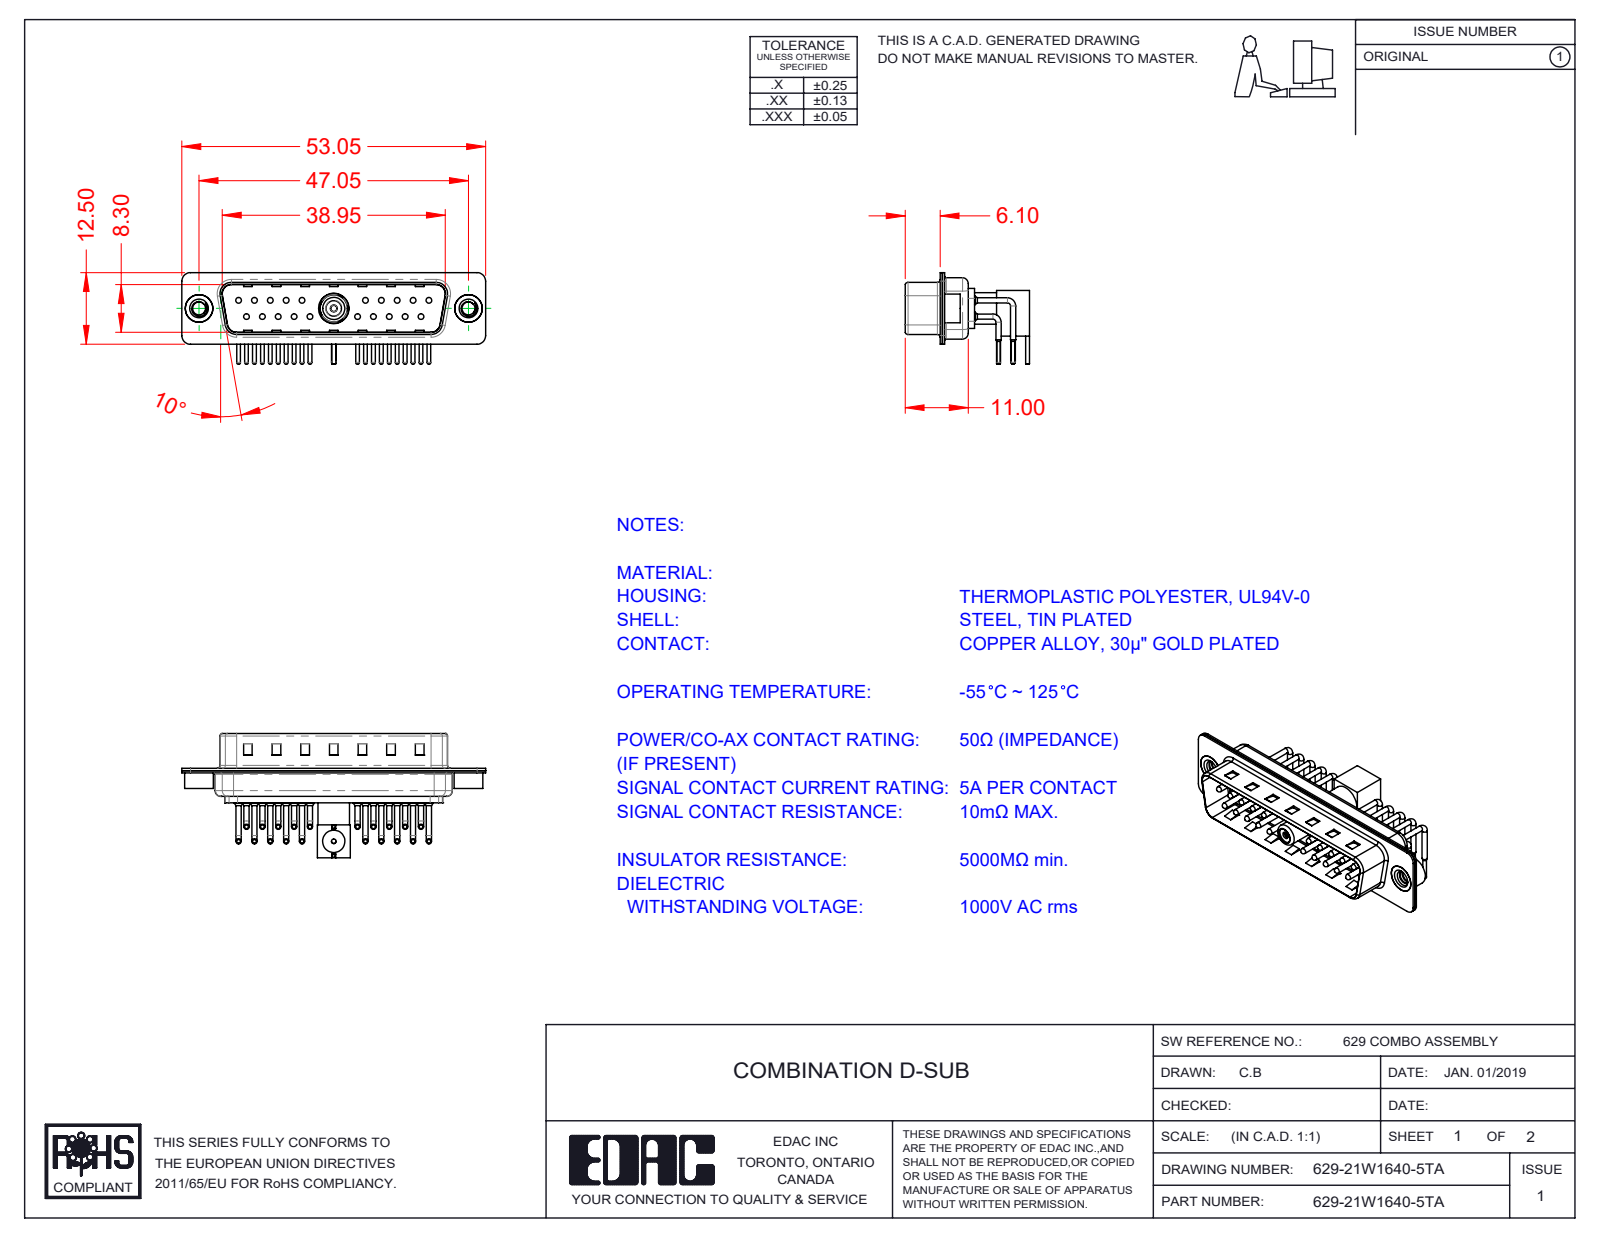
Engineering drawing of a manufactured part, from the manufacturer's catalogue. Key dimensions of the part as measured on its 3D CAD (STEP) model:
Part name (STEP PRODUCT): Insulator Socket; Locking Collar; 629Combo Contact Row 1; 629Combo Shell Rear_25 Contacts (+8 more)
STEP written by: SolidWorks 2020 (CONFIG_CONTROL_DESIGN)
Units: millimetres
Bodies: 32 solids, 2728 faces (1508 planar, 924 cylindrical, 296 other)
Overall size (bounding box): 53.05 × 21.71 × 16
Volume: 3 167 mm³ · Surface area: 8 440 mm²
Round holes (diameter × count): ⌀1.6 ×21, ⌀0.75 ×20, ⌀2 ×20, ⌀2.26 ×2, ⌀4 ×2, ⌀4.8 ×2, ⌀0.8 ×1, ⌀1.1 ×1, ⌀1.2 ×1, ⌀1.5 ×1, ⌀2.5 ×1, ⌀2.7 ×1
Round bosses / shafts (diameter × count): ⌀0.9 ×40, ⌀1.5 ×20, ⌀1 ×20, ⌀0.65 ×20, ⌀5 ×2, ⌀4.9 ×2, ⌀0.8 ×2, ⌀5.5 ×1
Partial cylindrical surfaces — rounded edges, fillets, slot ends (radius × count): R1.01 ×20, R1.5 ×16, R2 ×12, R0.5 ×8, R1.6 ×8, R0.25 ×4, R0.6 ×4, R0.65 ×4
Main face-to-face distances: 0.4, 0.8, 9.5, 9.1, 8.7, 9.9, 0.35, 0.75, 1.2, 6
Hole centre spacings: 3.16, 2.77, 5.54, 8.31, 5.04, 19.39, 20.97, 22.16
